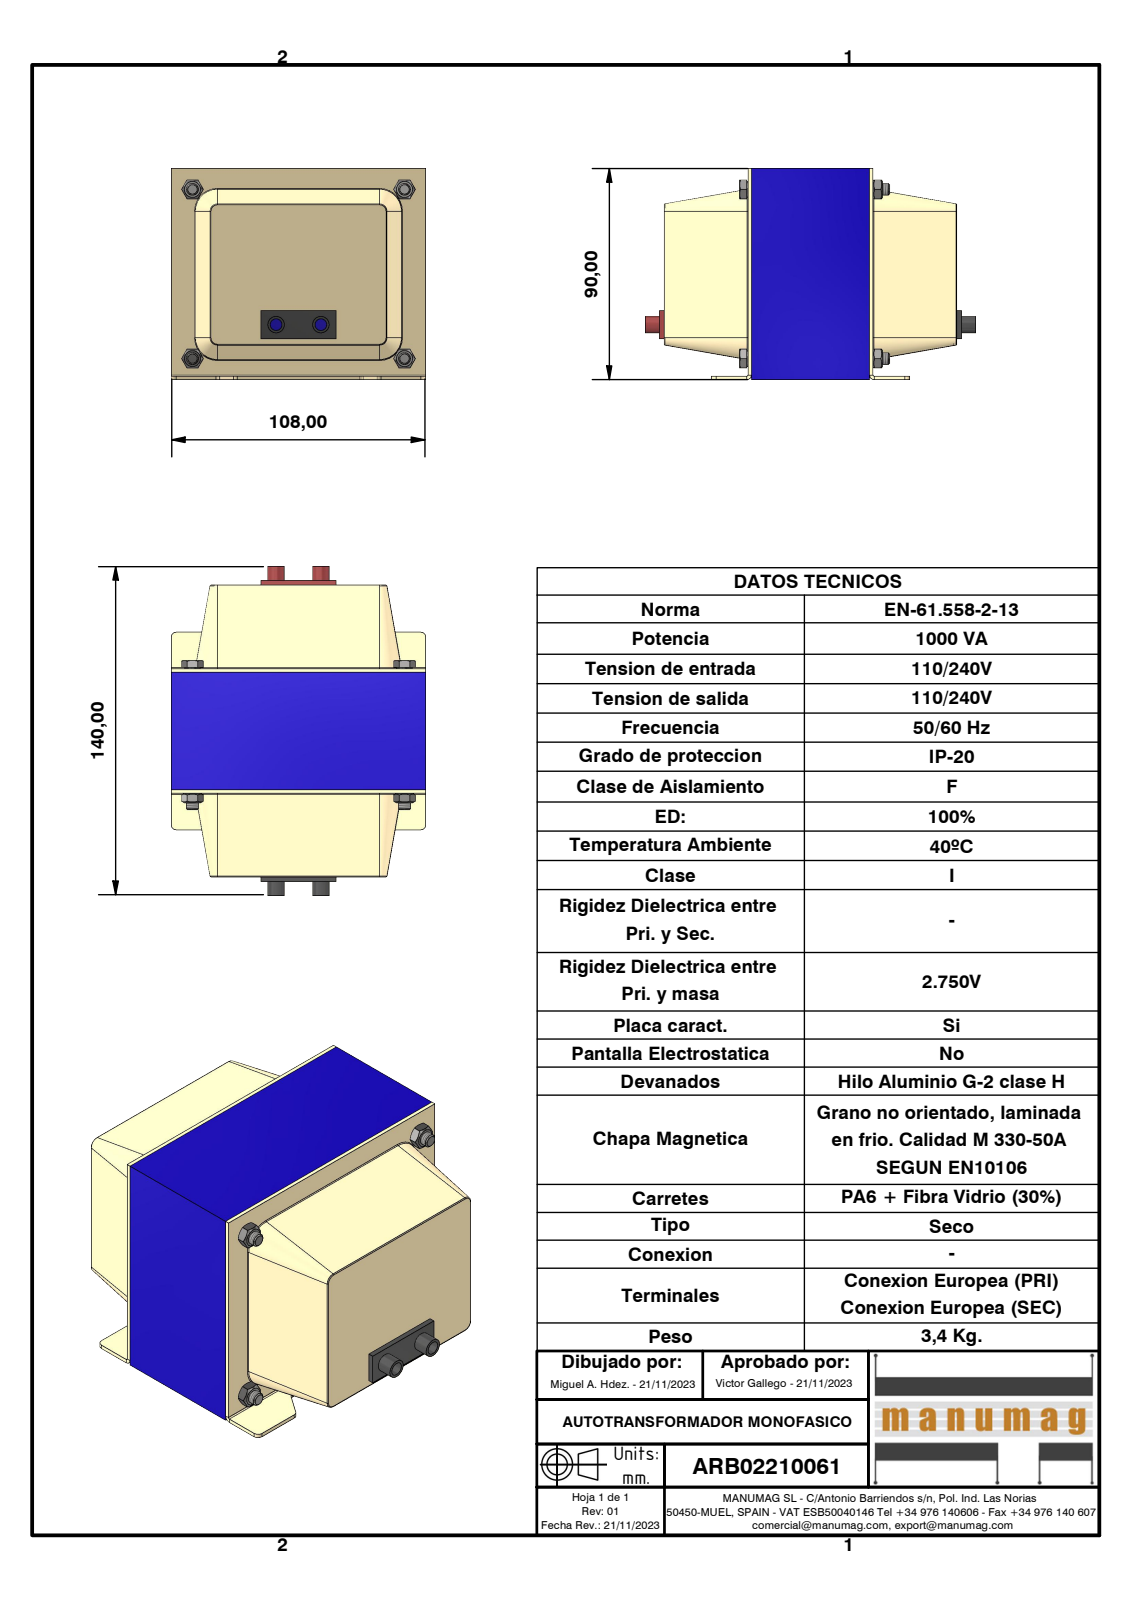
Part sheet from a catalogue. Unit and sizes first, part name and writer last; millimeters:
Units: millimetres
Overall size (bounding box): 140 × 108 × 90
Round holes (diameter × count): ⌀5 ×6, ⌀4.13 ×4, ⌀5.6 ×4
Round bosses / shafts (diameter × count): ⌀6.7 ×4, ⌀4.57 ×4, ⌀7 ×2
Partial cylindrical surfaces — rounded edges, fillets, slot ends (radius × count): R0.38 ×16, R2 ×14, R0.5 ×2
Main face-to-face distances: 1.5, 87, 35.5, 18, 72, 90, 50, 37, 36, 88.5
Hole centre spacings: 38.33, 56.39, 67.61, 72, 79.25, 90, 115.26, 19
Volume: 422 530 mm³ · Surface area: 137 856 mm²
Bodies: 13 solids, 310 faces (162 planar, 68 cylindrical, 80 other)
Part name (STEP PRODUCT): ARB02210061; TAPA RC36 RECEPTACULO; Receptaculo negro; Receptaculo Rojo (+3 more)
STEP written by: Autodesk Inventor 2023 (AUTOMOTIVE_DESIGN)
